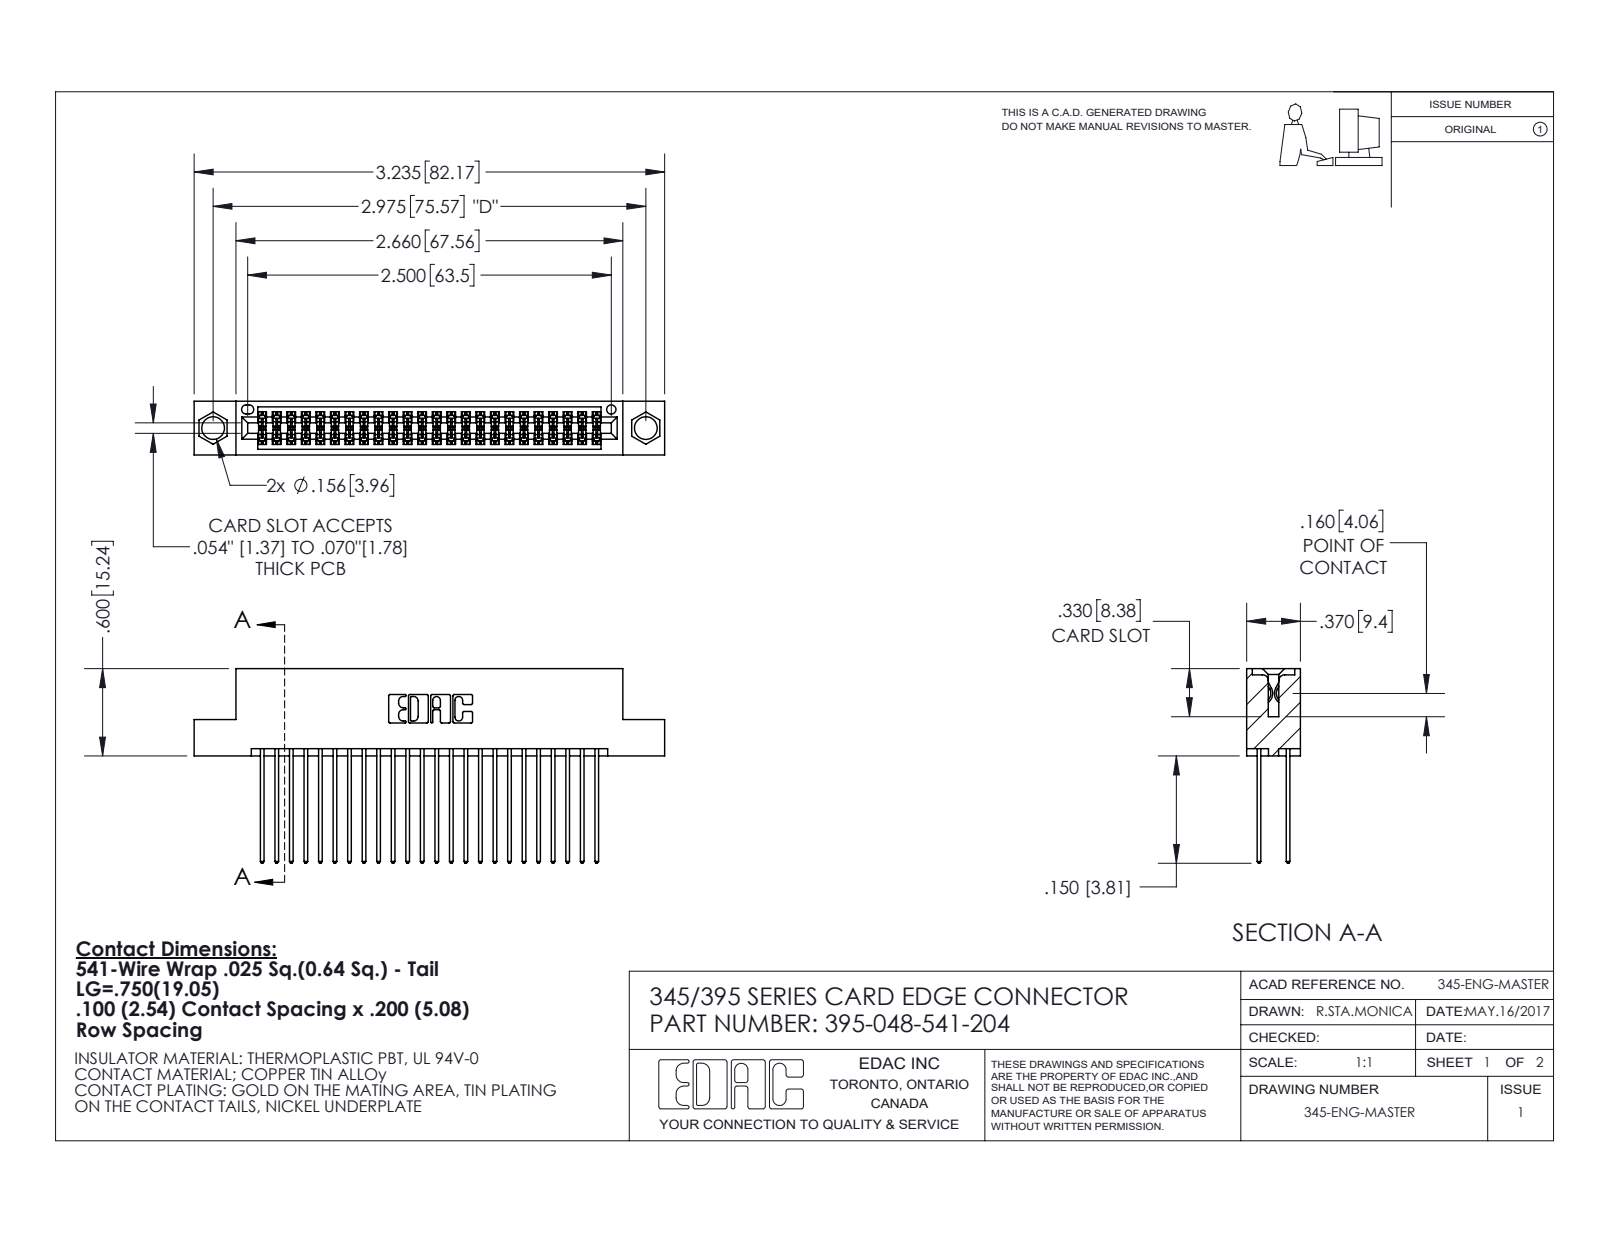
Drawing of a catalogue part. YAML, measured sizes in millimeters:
part_name: "345 Part_Flush Mounting Lugs - 0.156 Dia-TI; 395-048-541-204; 345-292-001_345-293-141"
step_written_by: "SolidWorks 2020 (CONFIG_CONTROL_DESIGN)"
units: millimeters
bodies: {solids: 49, faces: 2540, planar: 1678, cylindrical: 862, other: 0}
overall_size: [82.2, 34, 9.4]
volume: 7980
surface_area: 12600
round_holes:
  - {diameter: 4, count: 2}
  - {diameter: 1.6, count: 1}
partial_cylinders:
  - {radius: 0.2, count: 72}
  - {radius: 0.3, count: 48}
  - {radius: 0.3, count: 22}
  - {radius: 0.2, count: 6}
  - {radius: 0.8, count: 6}
  - {radius: 0.7, count: 3}
  - {radius: 0.4, count: 2}
  - {radius: 0.5, count: 2}
face_to_face_distances: [7.6, 1.8, 5.1, 2.5, 6.9, 0.6, 9.4, 5.7, 4.4, 3.8]
hole_center_spacings: [6.9, 69.6, 75.6]
